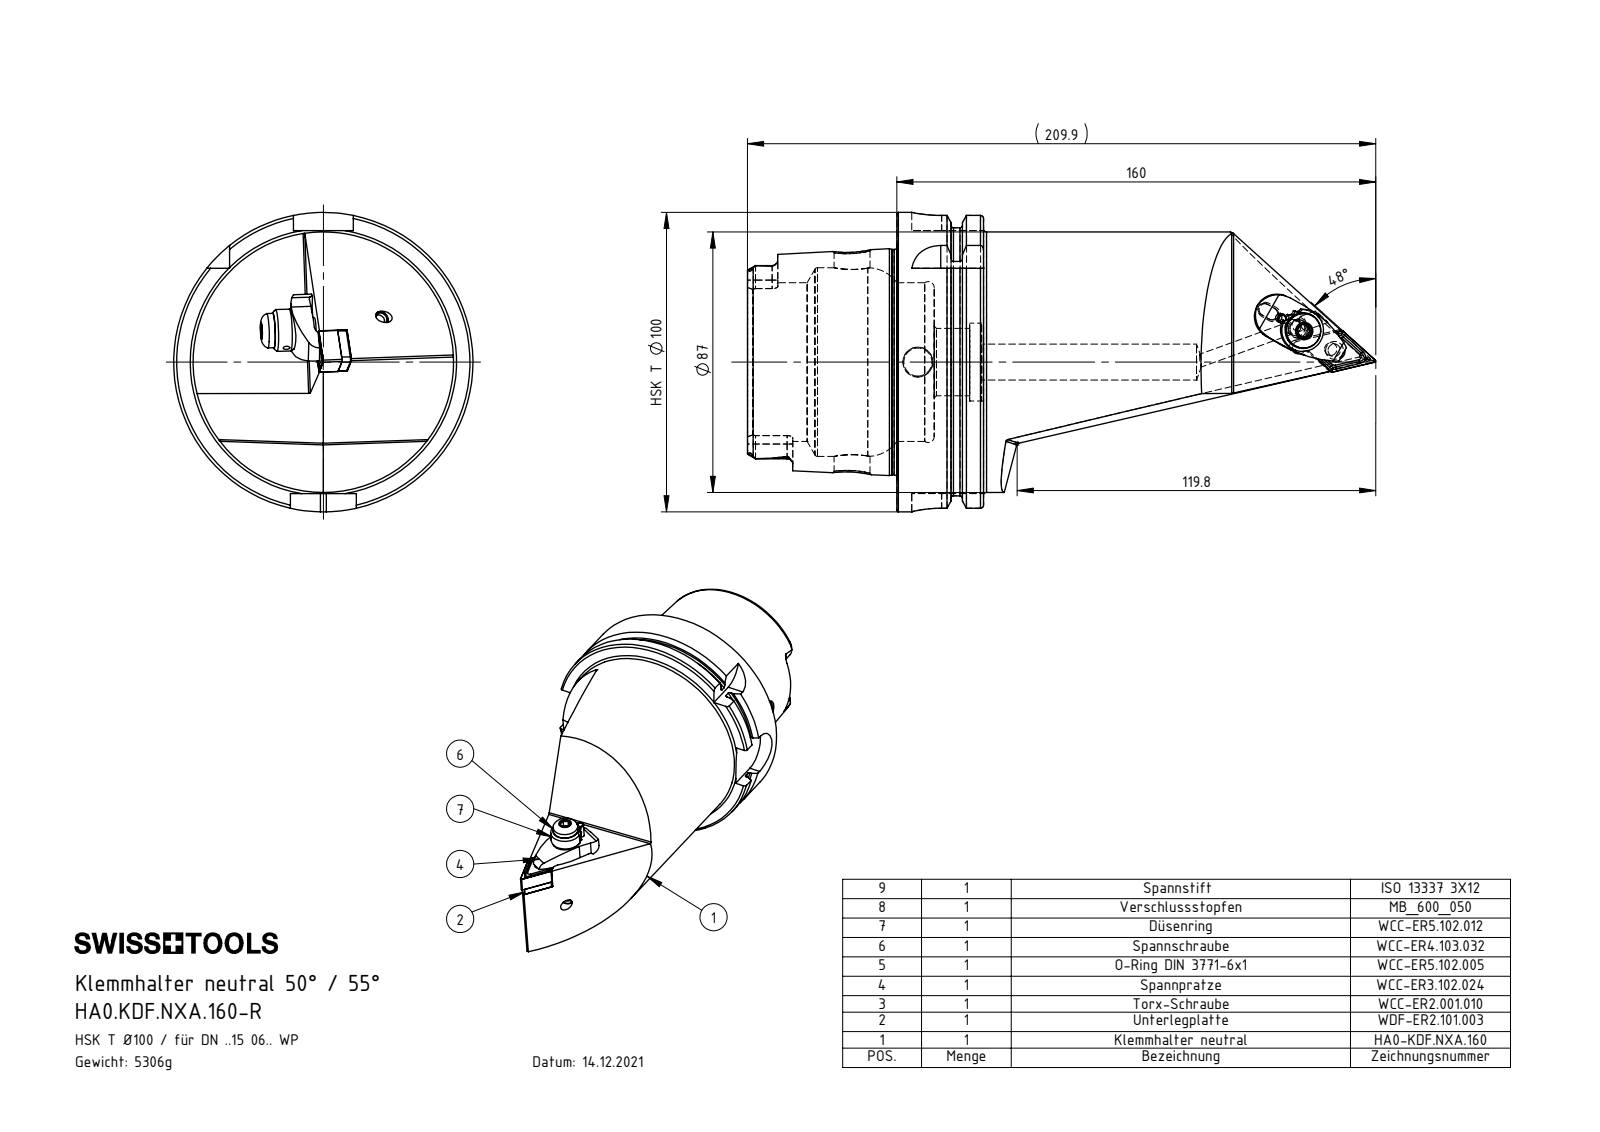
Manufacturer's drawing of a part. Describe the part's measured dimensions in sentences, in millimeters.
The part is named "WCC-ER5.102.005_A; WCC-ER4.103.032_A; WCC-ER5.102.012_B; WCC-ER3.102.024_C (+7 more)". Its 3-D file was written by "SolidWorks 2017 (AUTOMOTIVE_DESIGN)". It is 11 solids with 459 faces: 120 planar, 153 cylindrical and 186 other. Overall it measures 209.9 by 100 by 100 millimeters. Its volume is 676 907 cubic millimeters and its surface area 82 614 square millimeters. Round holes: 3 of diameter 2, 2 of diameter 4.2, 2 of diameter 5, 2 of diameter 7, 2 of diameter 12, 1 of diameter 2.4, 1 of diameter 3, 1 of diameter 4, 1 of diameter 5.16, 1 of diameter 6.2, 1 of diameter 6.4, 1 of diameter 8.5. Round bosses or shafts: 2 of diameter 5, 1 of diameter 100, 1 of diameter 91.95, 1 of diameter 87, 1 of diameter 75.26, 1 of diameter 14, 1 of diameter 11.5, 1 of diameter 7. Partial cylindrical surfaces (rounded edges, fillets, slot ends): 6 of radius 0.39, 6 of radius 1.9, 4 of radius 0.4, 4 of radius 1, 4 of radius 4.88, 4 of radius 10, 3 of radius 0.69, 3 of radius 0.69. The main face-to-face distances are 12.45, 16.5, 28.95, 49.9, 62.35, 78.85, 87.8, 78.2, 28.3, 15.85. The hole center spacings are 14.79, 14.99, 8.01, 8.21, 22.99, 23.
